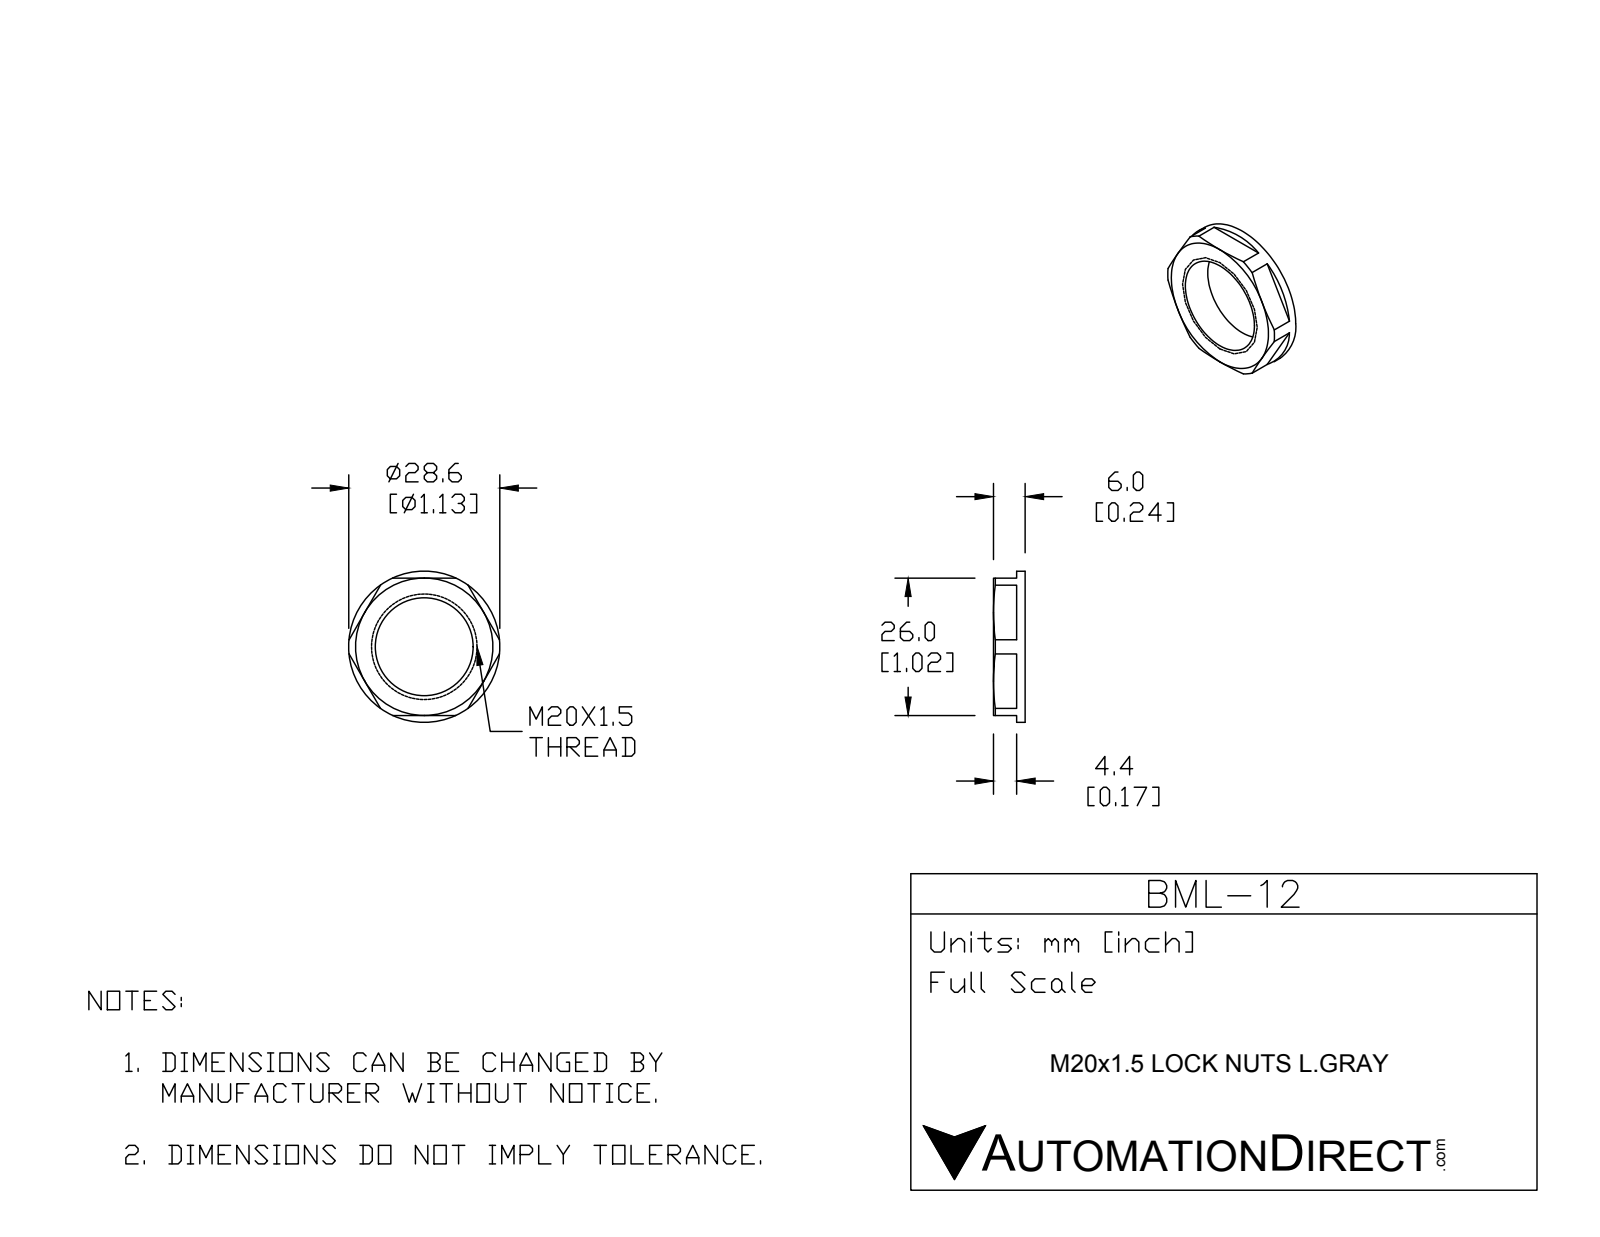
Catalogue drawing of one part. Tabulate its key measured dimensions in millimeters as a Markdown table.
| quantity | value |
| --- | --- |
| part name | BML-12 |
| STEP written by | SolidWorks 2015 (CONFIG_CONTROL_DESIGN) |
| units | millimeters |
| bodies | 1 solid, 33 faces (17 planar, 10 cylindrical, 6 other) |
| overall size | 28.6 × 28.6 × 6 |
| volume | 1 958 mm³ |
| surface area | 1 617 mm² |
| round holes (diameter × count) | 1.5 × 3, 18.5 × 1 |
| round bosses / shafts (diameter × count) | 28.6 × 1 |
| main face-to-face distances | 6, 26, 1.6, 4.4, 1.3, 5.7 |
| hole center spacings | 12.85, 22.26, 22.25 |
